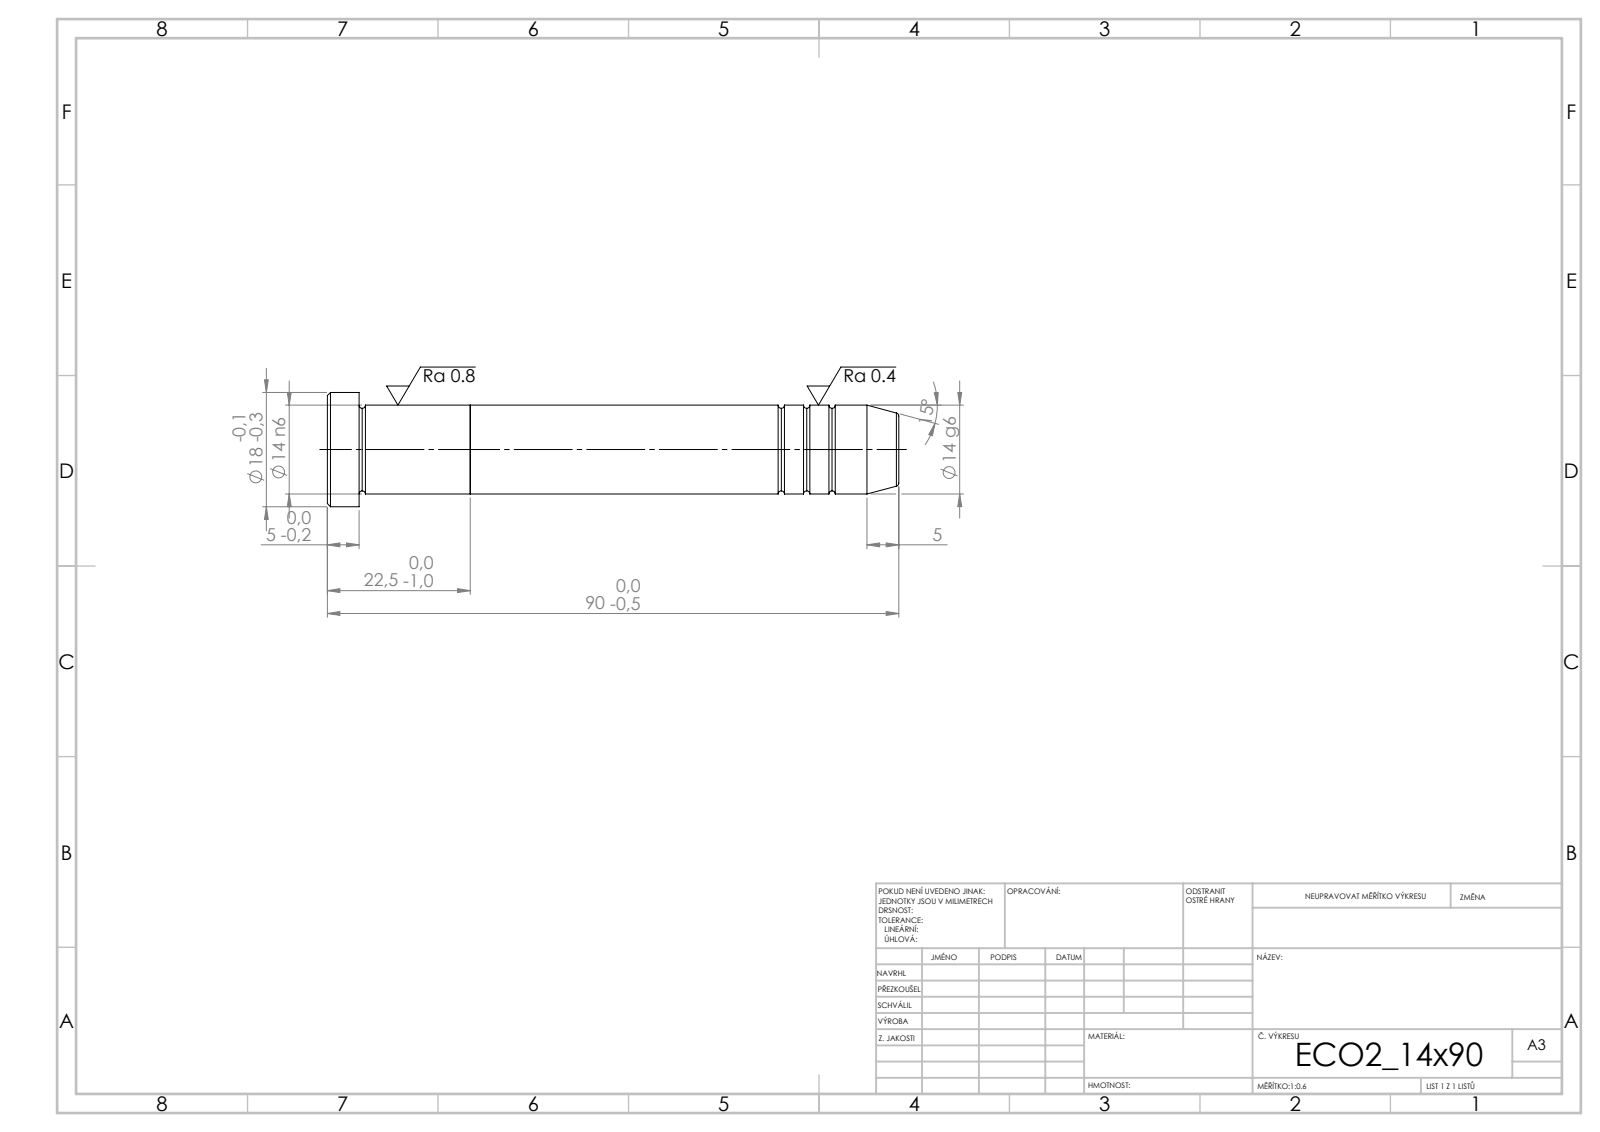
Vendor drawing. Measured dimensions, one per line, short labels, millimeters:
written by: SolidWorks 2019 (CONFIG_CONTROL_DESIGN)
unit: mm
bodies: 2 solids, 39 faces (5 planar, 12 cylindrical, 22 other)
size: 90 × 18 × 18
volume: 14 144 mm³; area: 4 838 mm²
bosses: 1× ⌀18, 1× ⌀14
face distances: 22.5, 17.5, 5, 67.5, 85, 90
